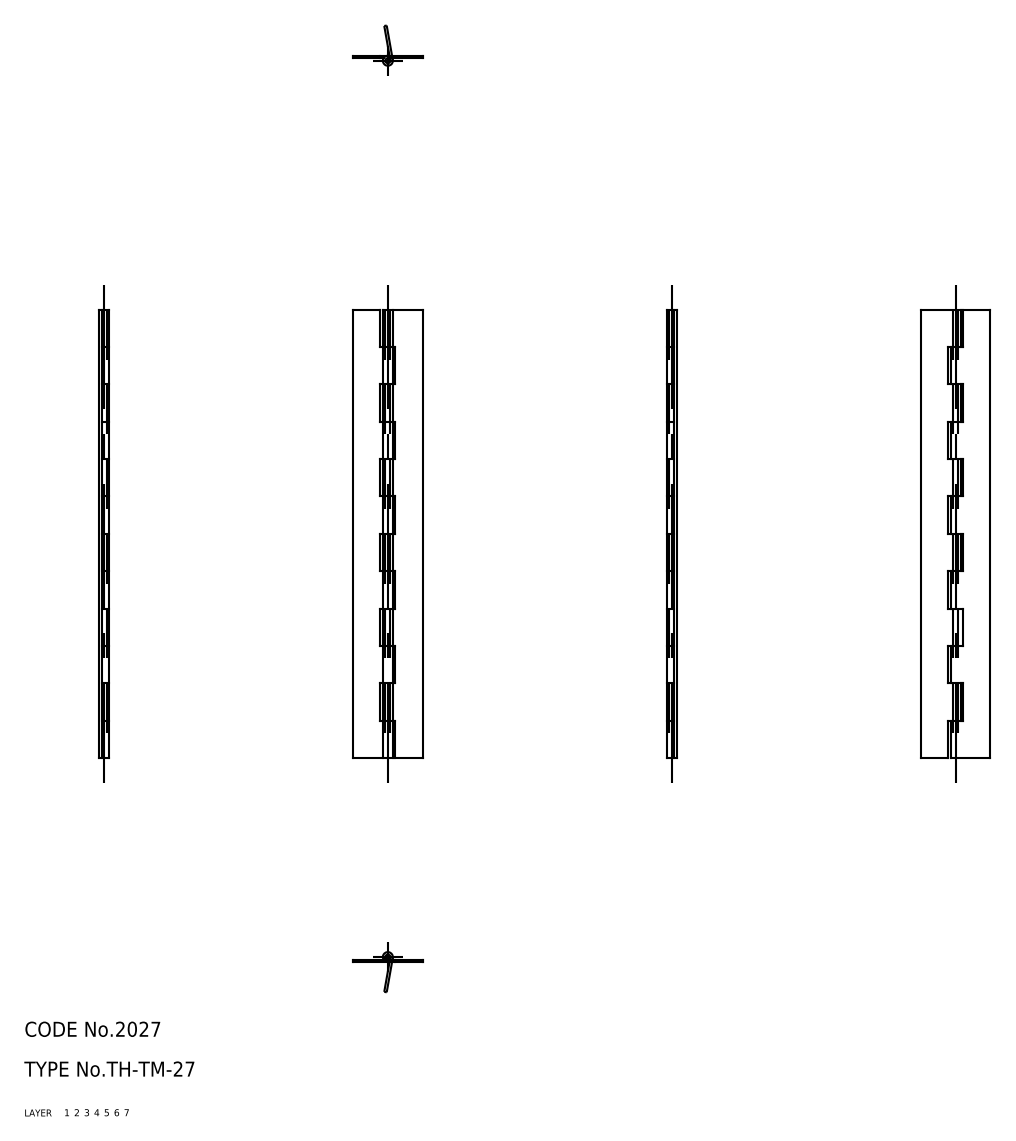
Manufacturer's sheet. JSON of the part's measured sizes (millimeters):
{"part_name": "hinge piece_B; hinge piece_A; shaft; TH_TM_27_22317_36", "step_written_by": "CADfix (AUTOMOTIVE_DESIGN)", "units": "millimeters", "bodies": {"solids": 3, "faces": 84, "planar": 0, "cylindrical": 0, "other": 84}, "overall_size": [90, 14, 2], "volume_mm3": 808, "surface_area_mm2": 3489}
